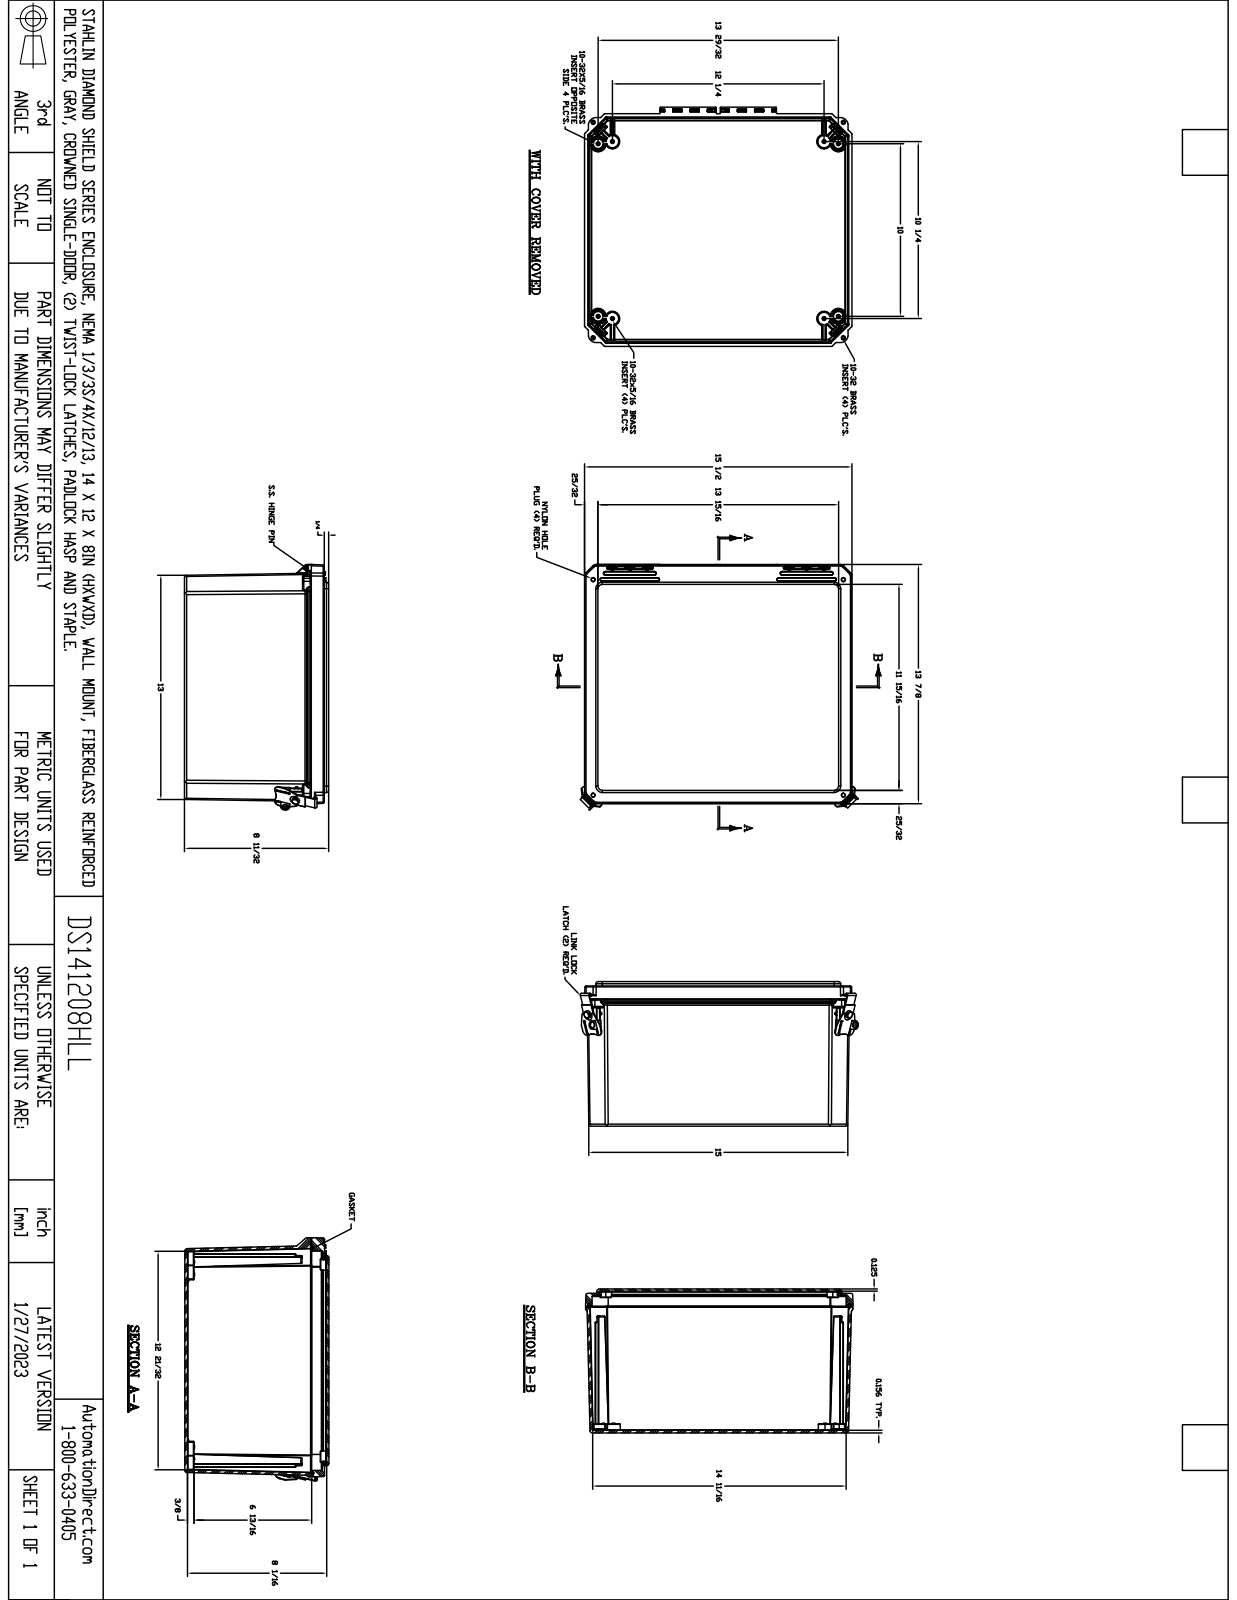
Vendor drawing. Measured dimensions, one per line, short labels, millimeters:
name: FR141208HLL
written by: SolidWorks 2018 (AUTOMOTIVE_DESIGN)
unit: mm
bodies: 37 solids, 2349 faces (820 planar, 920 cylindrical, 609 other)
size: 417.8 × 364.7 × 219.7
volume: 2 366 000 mm³; area: 1 195 000 mm²
holes: 16× ⌀4, 8× ⌀3.9, 4× ⌀2.5, 4× ⌀3.8, 4× ⌀6.4, 4× ⌀6.4, 2× ⌀1.3, 2× ⌀3, 2× ⌀5.6, 2× ⌀5.8, 2× ⌀8, 2× ⌀9.2
bosses: 16× ⌀6.2, 4× ⌀5.3, 4× ⌀5.1, 3× ⌀3.4, 2× ⌀15.2, 2× ⌀11, 2× ⌀1.3
rounds: 195× R0.3, 88× R0.1, 49× R0.5, 45× R0.8, 34× R3.2, 28× R1, 24× R0.8, 24× R2.3
face distances: 4, 3.2, 207.9, 211.9, 4.1, 4, 208.7, 204.7, 6.4, 3.2
hole spacings: 351.4, 20.1, 21, 32.5, 32.5, 40.2, 40.2, 258
